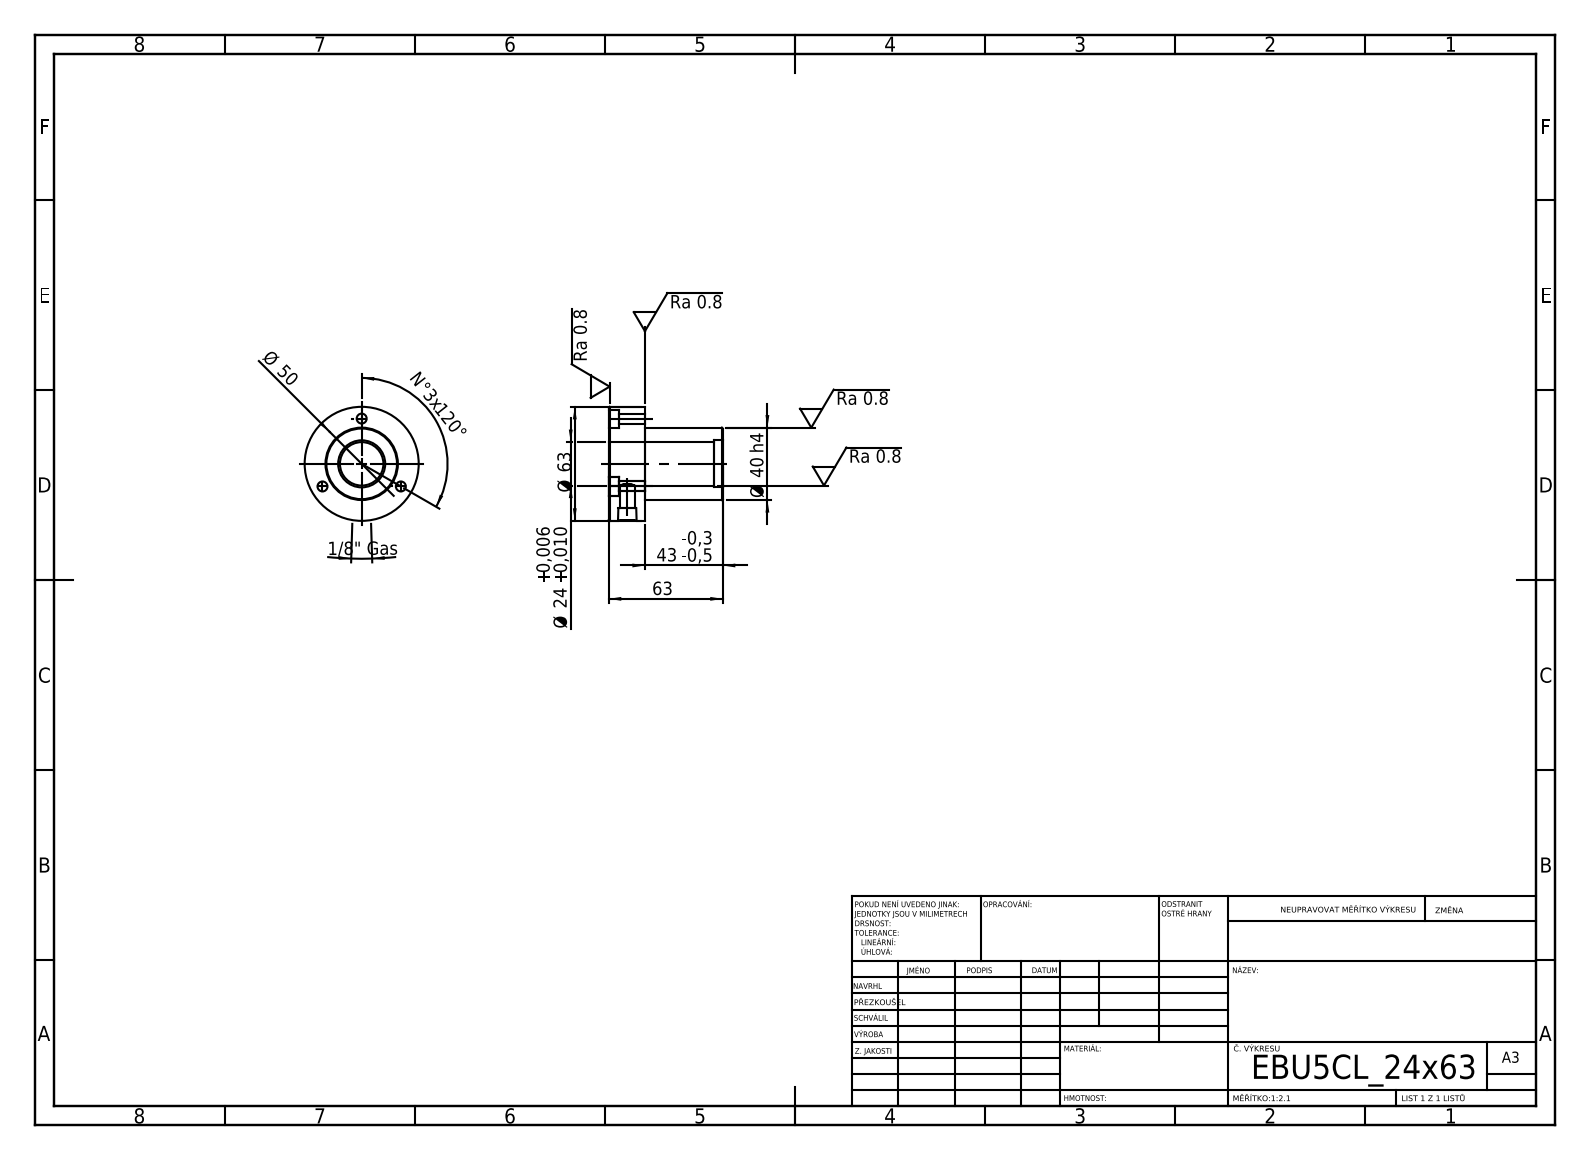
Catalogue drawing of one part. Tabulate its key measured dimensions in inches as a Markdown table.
| quantity | value |
| --- | --- |
| STEP written by | SolidWorks 2019 (CONFIG_CONTROL_DESIGN) |
| units | inches |
| bodies | 1 solid, 36 faces (8 planar, 22 cylindrical, 6 other) |
| overall size | 2.48 × 2.48 × 2.48 |
| volume | 5.118 in³ |
| surface area | 32.45 in² |
| round holes (diameter × count) | 0.217 × 3, 0.394 × 3, 0.332 × 1, 0.945 × 1, 1.024 × 1 |
| round bosses / shafts (diameter × count) | 2.48 × 1, 1.575 × 1 |
| main face-to-face distances | 0.787, 1.693, 2.48, 2.268, 0.575, 0.213, 0.197, 1.496, 2.071, 2.283 |
| hole center spacings | 0.984, 1.705 |
